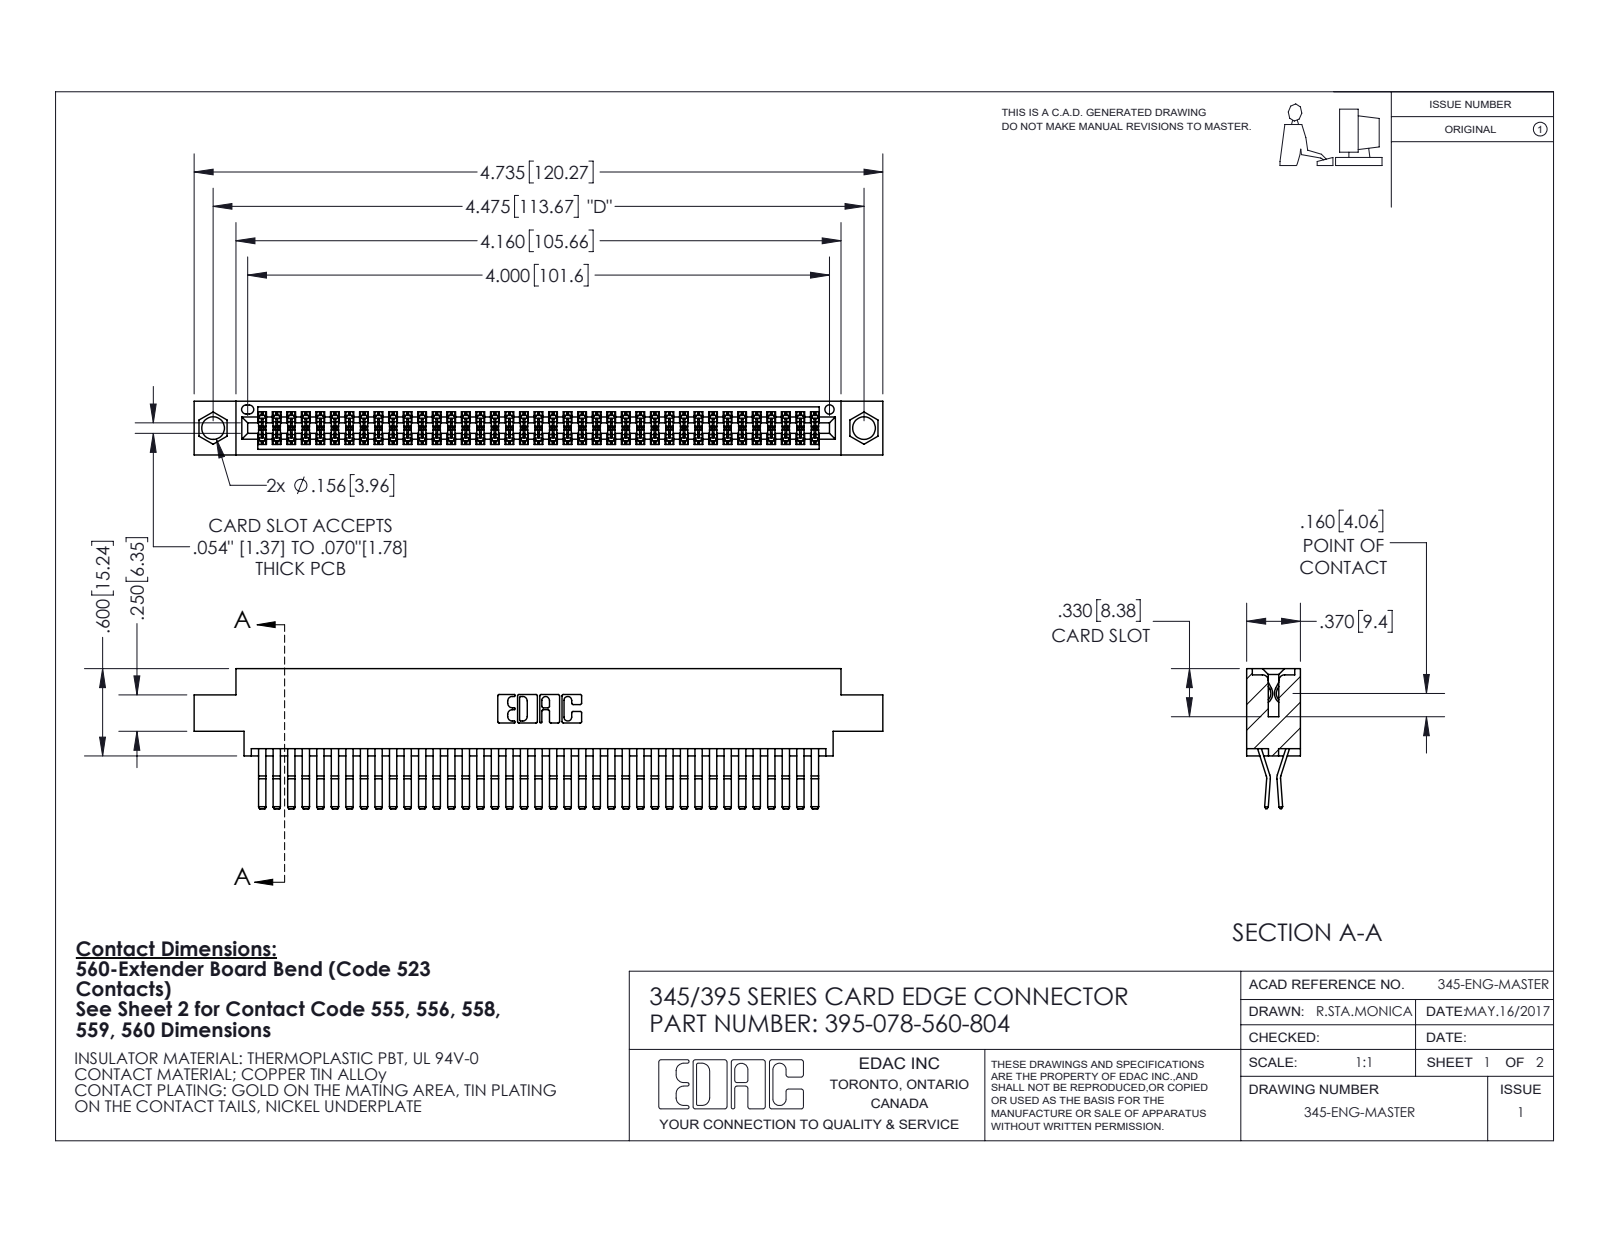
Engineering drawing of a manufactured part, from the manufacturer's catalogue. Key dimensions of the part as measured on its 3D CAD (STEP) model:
Part name (STEP PRODUCT): 345-292-001_560 Tail; 345 Part_0.170 Offset - 0.156 Dia-TI; 395-078-560-804
STEP written by: SolidWorks 2020 (CONFIG_CONTROL_DESIGN)
Units: inches
Bodies: 79 solids, 4200 faces (2672 planar, 1528 cylindrical, 0 other)
Overall size (bounding box): 4.735 × 0.962 × 0.37
Volume: 0.729 in³ · Surface area: 29.31 in²
Round holes (diameter × count): ⌀0.156 ×2, ⌀0.064 ×1
Partial cylindrical surfaces — rounded edges, fillets, slot ends (radius × count): R0.006 ×117, R0.01 ×22, R0.007 ×6, R0.031 ×6, R0.026 ×3, R0.01 ×2, R0.014 ×2, R0.019 ×2
Main face-to-face distances: 0.025, 0.298, 0.072, 0.37, 0.2, 0.098, 0.272, 0.225, 0.175, 0.149
Hole centre spacings: 0.27, 4.239, 4.475
